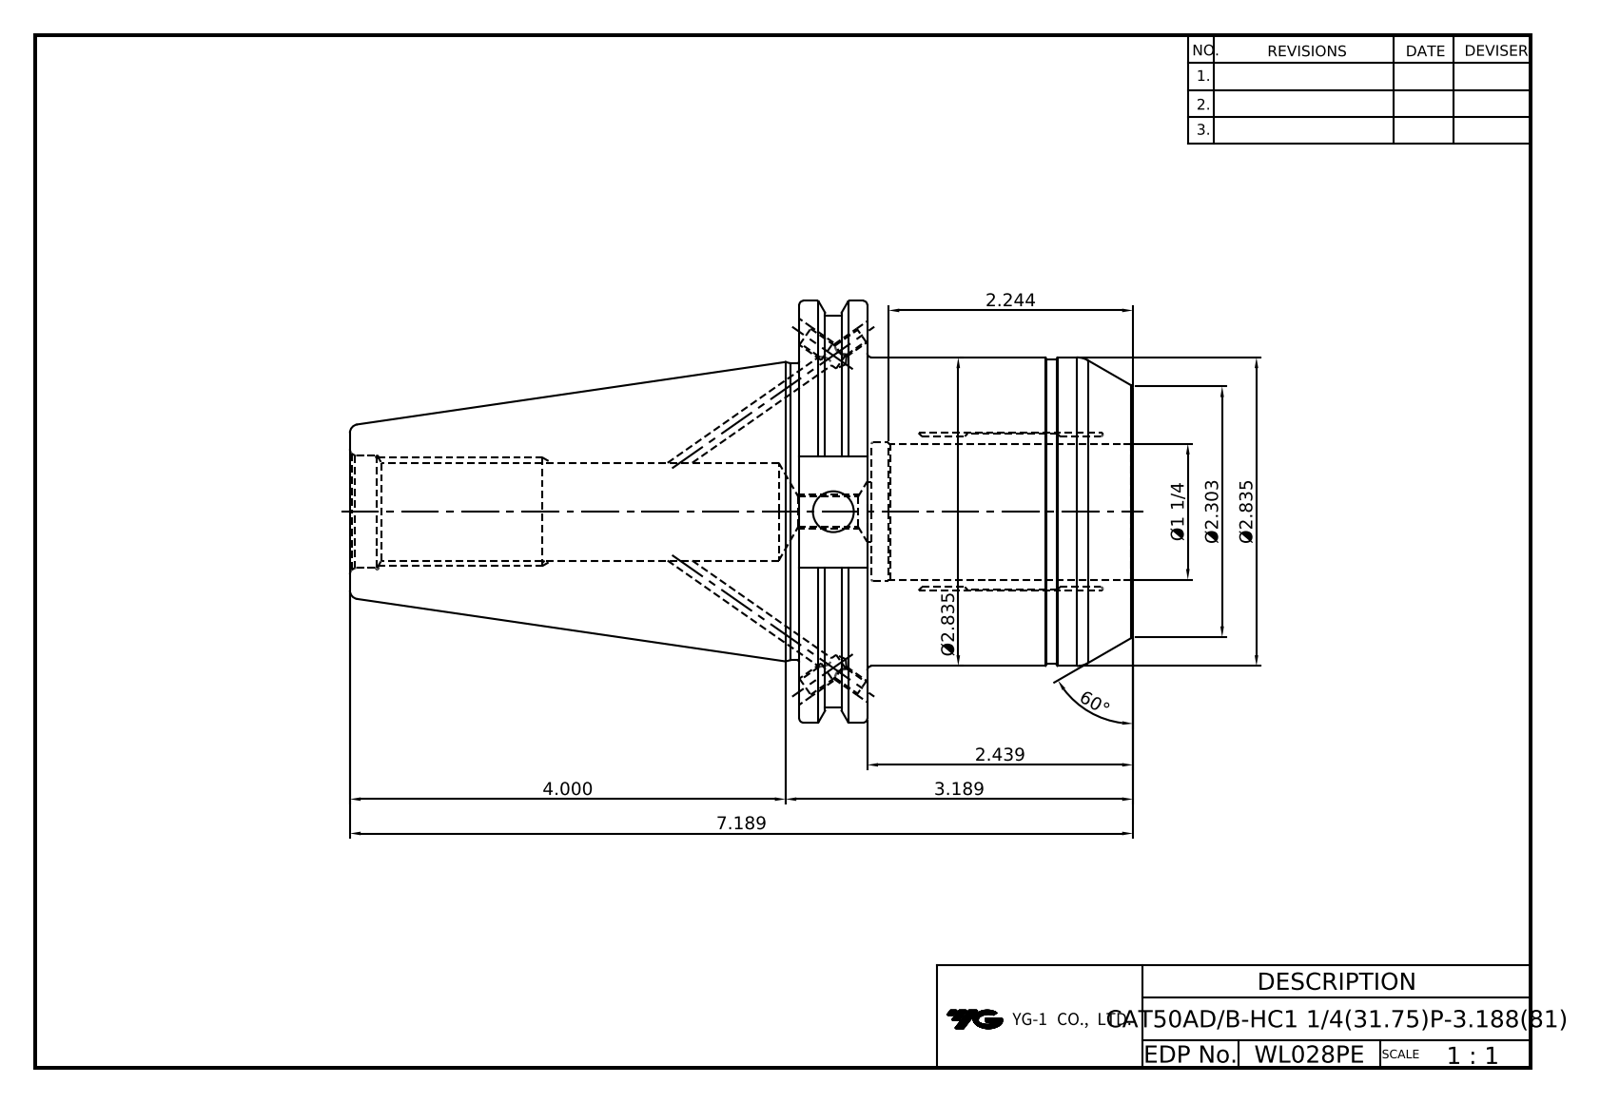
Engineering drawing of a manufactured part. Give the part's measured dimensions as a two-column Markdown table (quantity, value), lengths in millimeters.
| quantity | value |
| --- | --- |
| part name | LO-CAT50ADB-HC31.75P-81 |
| STEP written by | Autodesk Inventor 2025 (AUTOMOTIVE_DESIGN) |
| units | millimeters |
| bodies | 1 solid, 87 faces (29 planar, 30 cylindrical, 28 other) |
| overall size | 182.6 × 98.42 × 94.69 |
| volume | 518 188 mm³ |
| surface area | 63 928 mm² |
| round holes (diameter × count) | 4.13 × 4, 5 × 4, 6.92 × 1, 9.53 × 1, 14 × 1, 21.97 × 1, 26.2 × 1, 31.75 × 1, 32.55 × 1 |
| round bosses / shafts (diameter × count) | 98.42 × 1, 91.29 × 1, 72 × 1, 71 × 1, 69.25 × 1 |
| partial cylindrical surfaces (radius × count) | 12.95 × 1 |
| main face-to-face distances | 15.88, 77.83, 61.95, 16.83, 0.95, 61, 104.77, 120.65, 121.6, 182.6 |
| hole center spacings | 59.7 |
